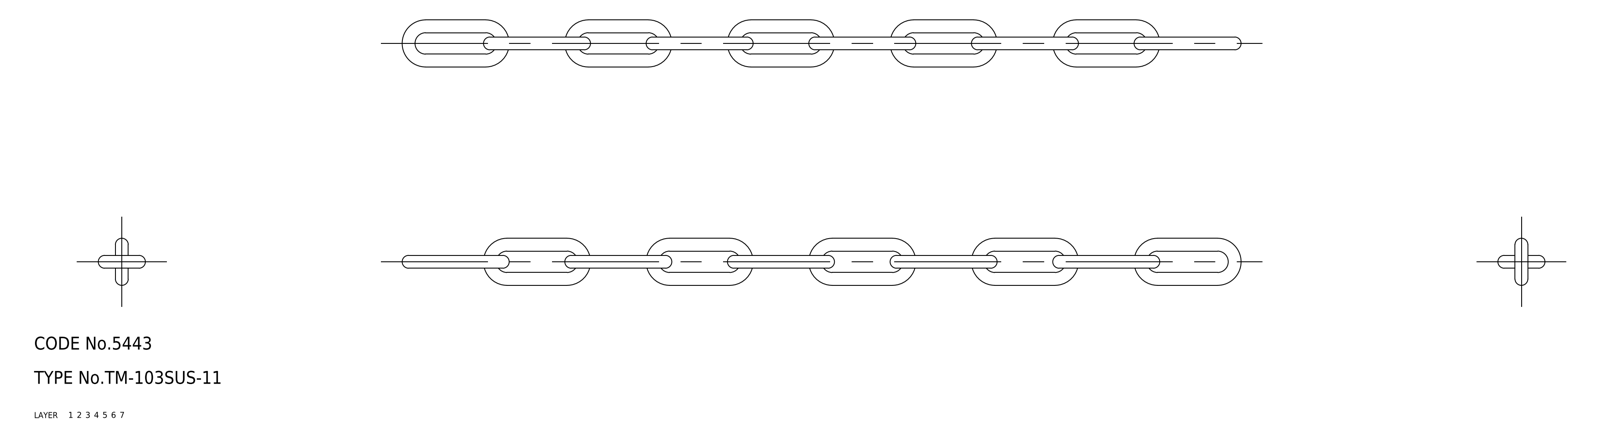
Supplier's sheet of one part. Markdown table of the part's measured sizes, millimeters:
| quantity | value |
| --- | --- |
| part name | chain; TM_103SUS_11_11384_36 |
| STEP written by | CADfix (AUTOMOTIVE_DESIGN) |
| units | millimeters |
| bodies | 10 solids, 80 faces (0 planar, 0 cylindrical, 80 other) |
| overall size | 196 × 11 × 11 |
| volume | 3 755 mm³ |
| surface area | 5 008 mm² |
